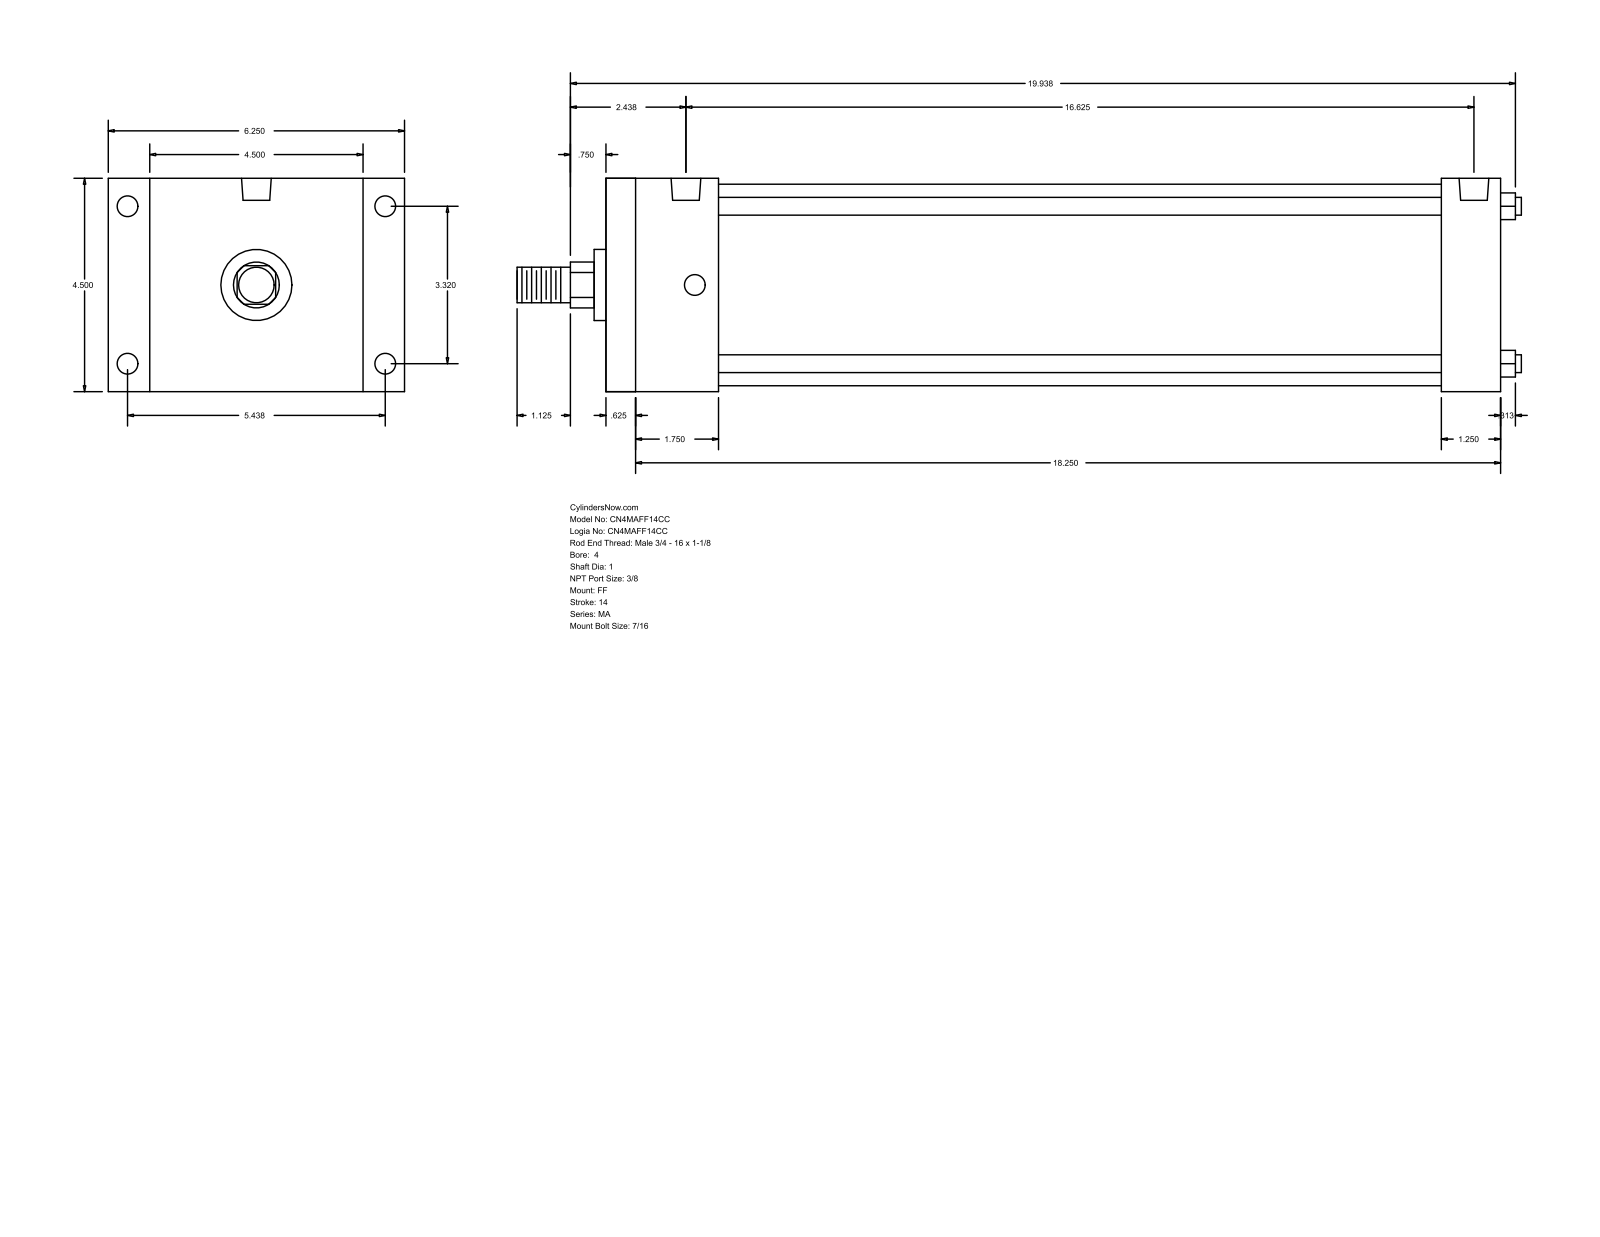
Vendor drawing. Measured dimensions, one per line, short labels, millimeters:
name: MA_FF__0400_1
written by: GSSL Pune (CONFIG_CONTROL_DESIGN)
unit: mm
bodies: 0 solids, 92 faces (64 planar, 28 cylindrical, 0 other)
size: 538.16 × 158.75 × 114.3
holes: 8× ⌀11.11, 2× ⌀15.93
bosses: 4× ⌀9.53, 1× ⌀107.95, 1× ⌀38.1, 1× ⌀25.4, 1× ⌀19.05
rounds: 1× R12.29
face distances: 114.3, 479.43, 15.87, 463.56, 22.23, 136.53, 447.68, 431.81, 31.75, 60.33
hole spacings: 4.76, 84.32, 138.12, 161.82, 412.76, 417.52, 422.28
